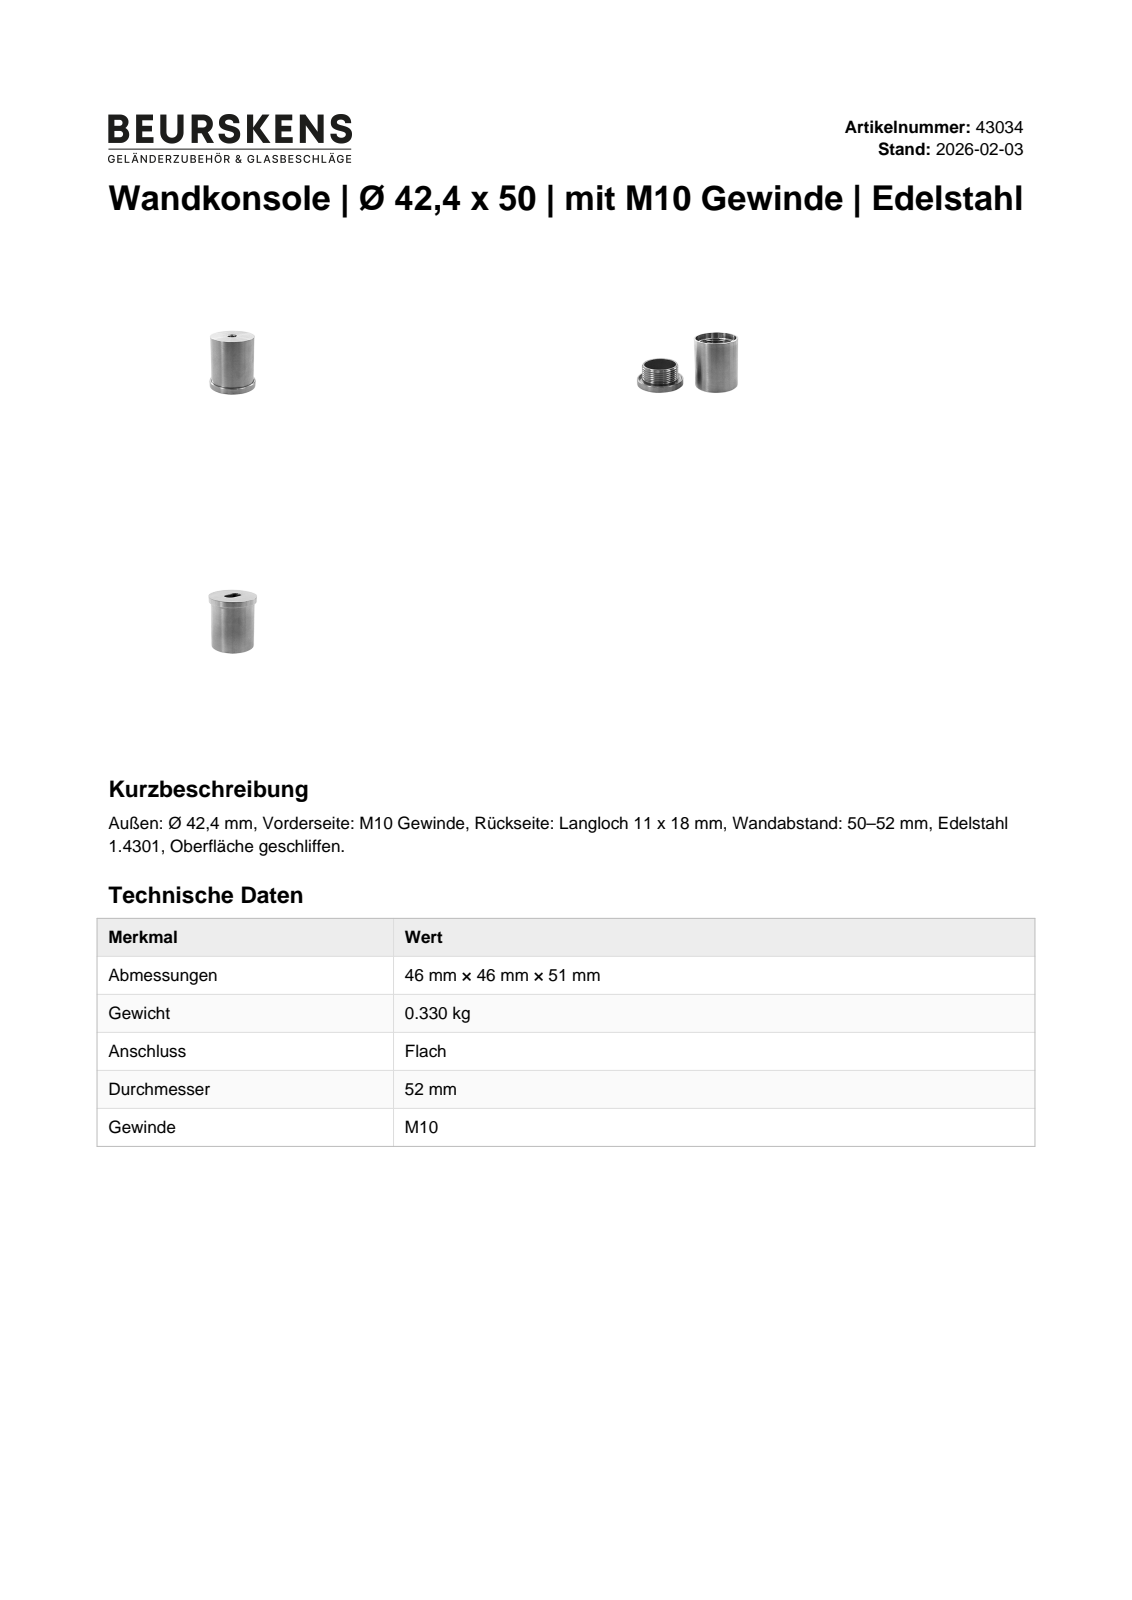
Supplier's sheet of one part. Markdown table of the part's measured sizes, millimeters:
| quantity | value |
| --- | --- |
| part name | 43034; 43034 Boden; 43034 Kopf |
| STEP written by | Autodesk Inventor 2023 (AUTOMOTIVE_DESIGN) |
| units | millimeters |
| bodies | 2 solids, 23 faces (11 planar, 10 cylindrical, 2 other) |
| overall size | 48 × 46 × 46 |
| volume | 46 130 mm³ |
| surface area | 20 278 mm² |
| round holes (diameter × count) | 10 × 1, 23 × 1, 32 × 1, 36 × 1, 44 × 1 |
| round bosses / shafts (diameter × count) | 46 × 1, 42.4 × 1 |
| partial cylindrical surfaces (radius × count) | 5.5 × 2 |
| main face-to-face distances | 1, 48, 18, 47, 17, 19, 2, 46, 29, 11 |
